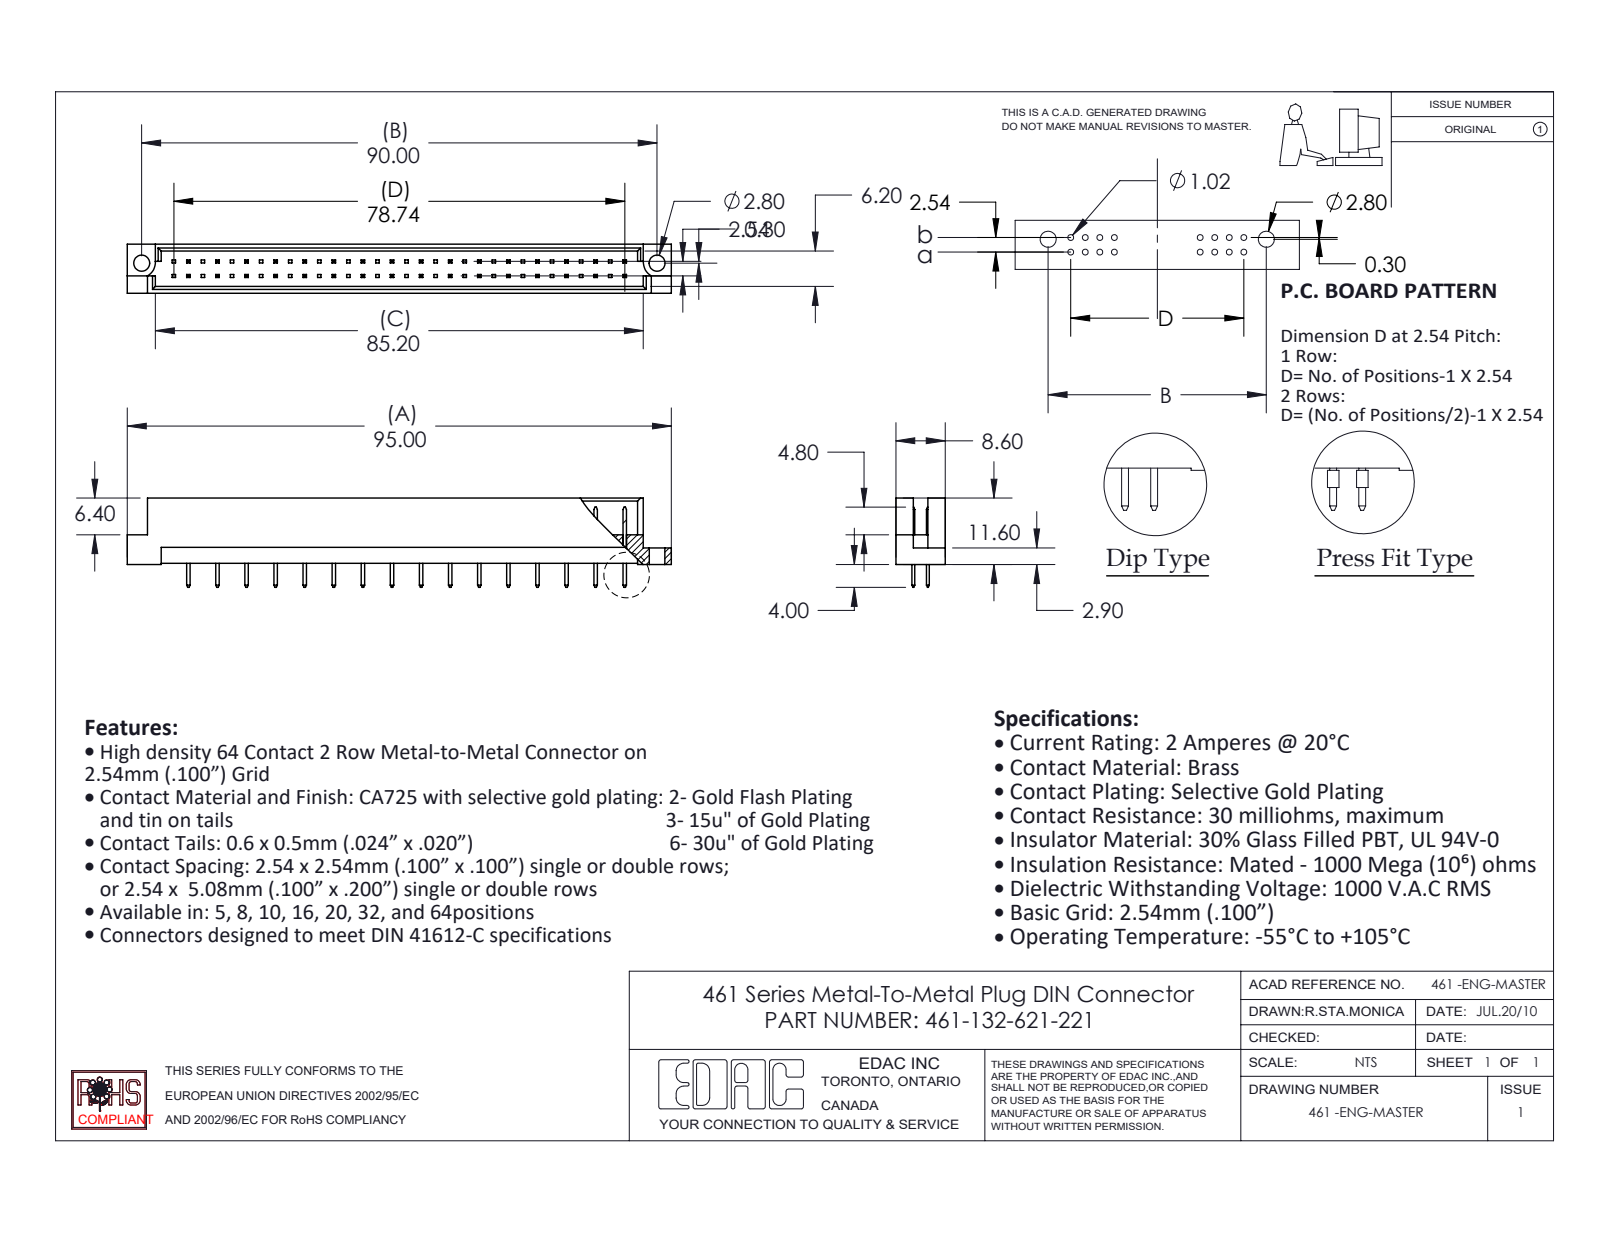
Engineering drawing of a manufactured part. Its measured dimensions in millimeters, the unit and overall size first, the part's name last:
Units: millimetres
Overall size (bounding box): 95 × 15.6 × 8.6
Round holes (diameter × count): ⌀2.8 ×2
Partial cylindrical surfaces — rounded edges, fillets, slot ends (radius × count): R2.8 ×2
Main face-to-face distances: 1.2, 7.4, 8.6, 6.2, 5, 2.54, 3.28, 5.32, 2.08, 4.12
Hole centre spacings: 90
Volume: 4 787 mm³ · Surface area: 6 645 mm²
Bodies: 33 solids, 753 faces (746 planar, 7 cylindrical, 0 other)
Part name (STEP PRODUCT): 461-132-621-221; 461-290_21; 461 Part_64
STEP written by: SolidWorks 2020 (CONFIG_CONTROL_DESIGN)
